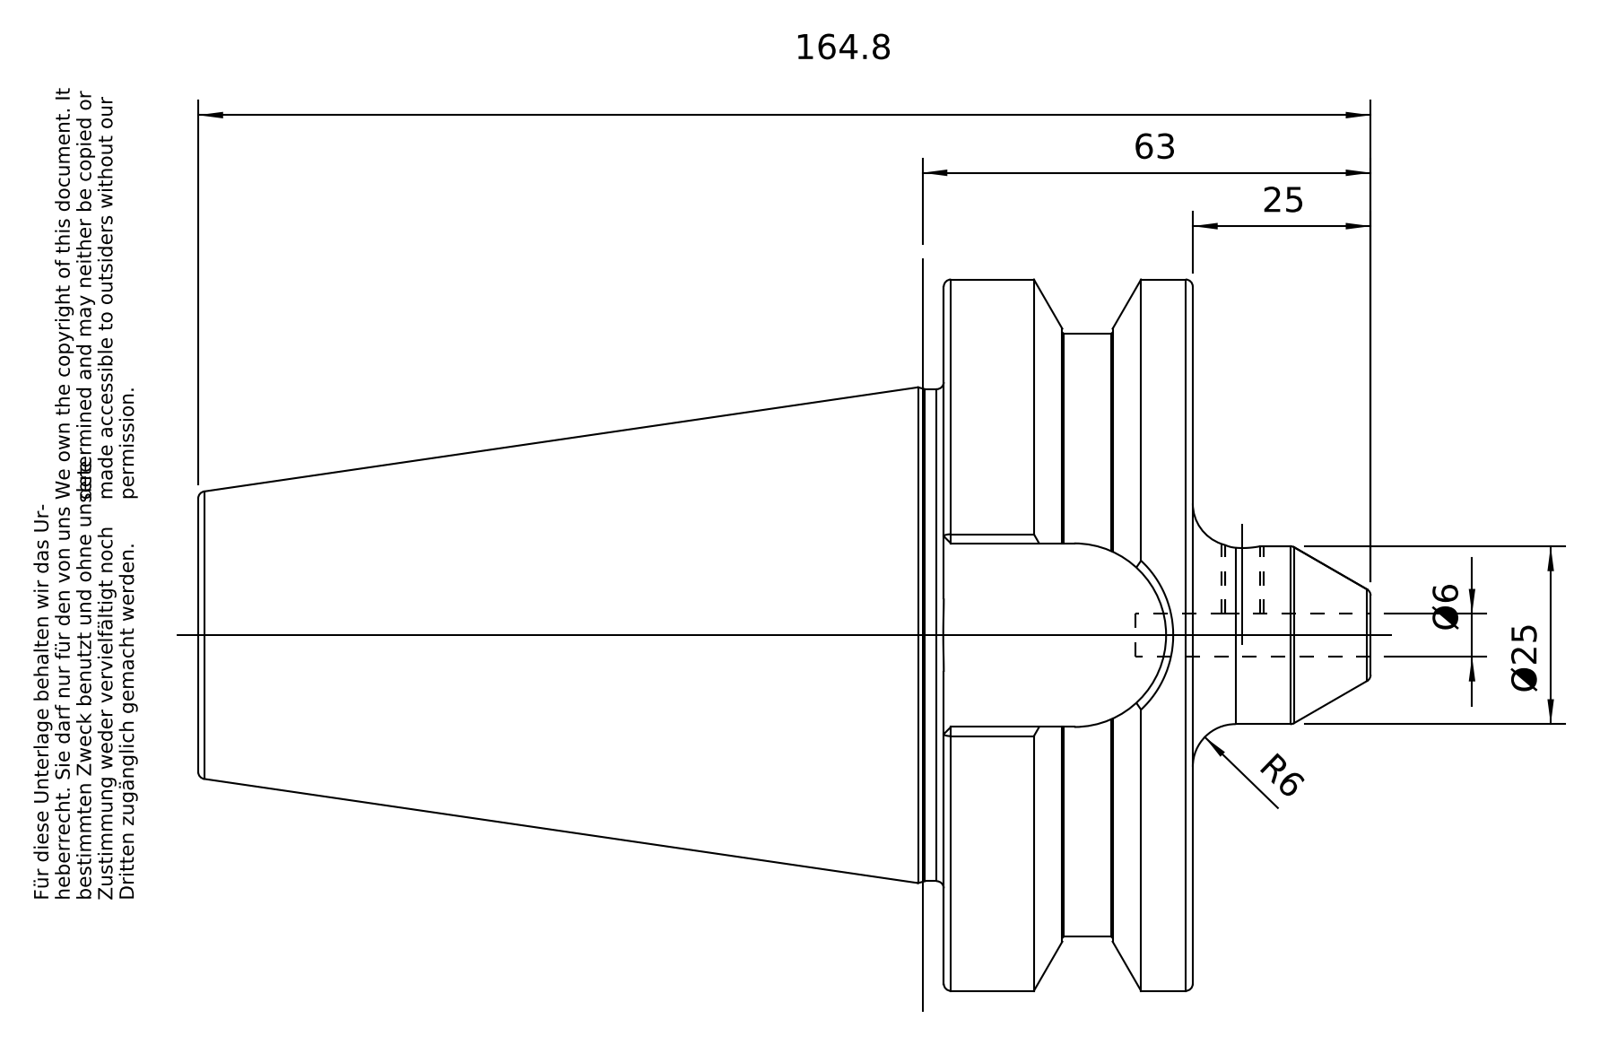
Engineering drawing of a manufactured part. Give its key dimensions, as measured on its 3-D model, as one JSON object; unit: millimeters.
{"part_name": "50-500-06", "step_written_by": "PRO/ENGINEER BY PARAMETRIC TECHNOLOGY CORPORATION, 2010430 (CONFIG_CONTROL_DESIGN)", "units": "millimeters", "bodies": {"solids": 1, "faces": 102, "planar": 26, "cylindrical": 26, "other": 50}, "overall_size": [164.8, 99.97, 99.97], "volume_mm3": 477585, "surface_area_mm2": 54062, "round_holes": [[6, 2], [5, 1], [20.75, 1], [25.02, 1], [25.7, 1]], "round_bosses_or_shafts": [[99.97, 1], [84.75, 1], [69.15, 1], [25, 1], [24.01, 1]], "partial_cylinders_radius": [[12.9, 1]], "face_to_face_distances": [35, 70.4, 104.8, 139.8, 25.8, 48, 56.8, 91.8, 128.54, 80.54]}
